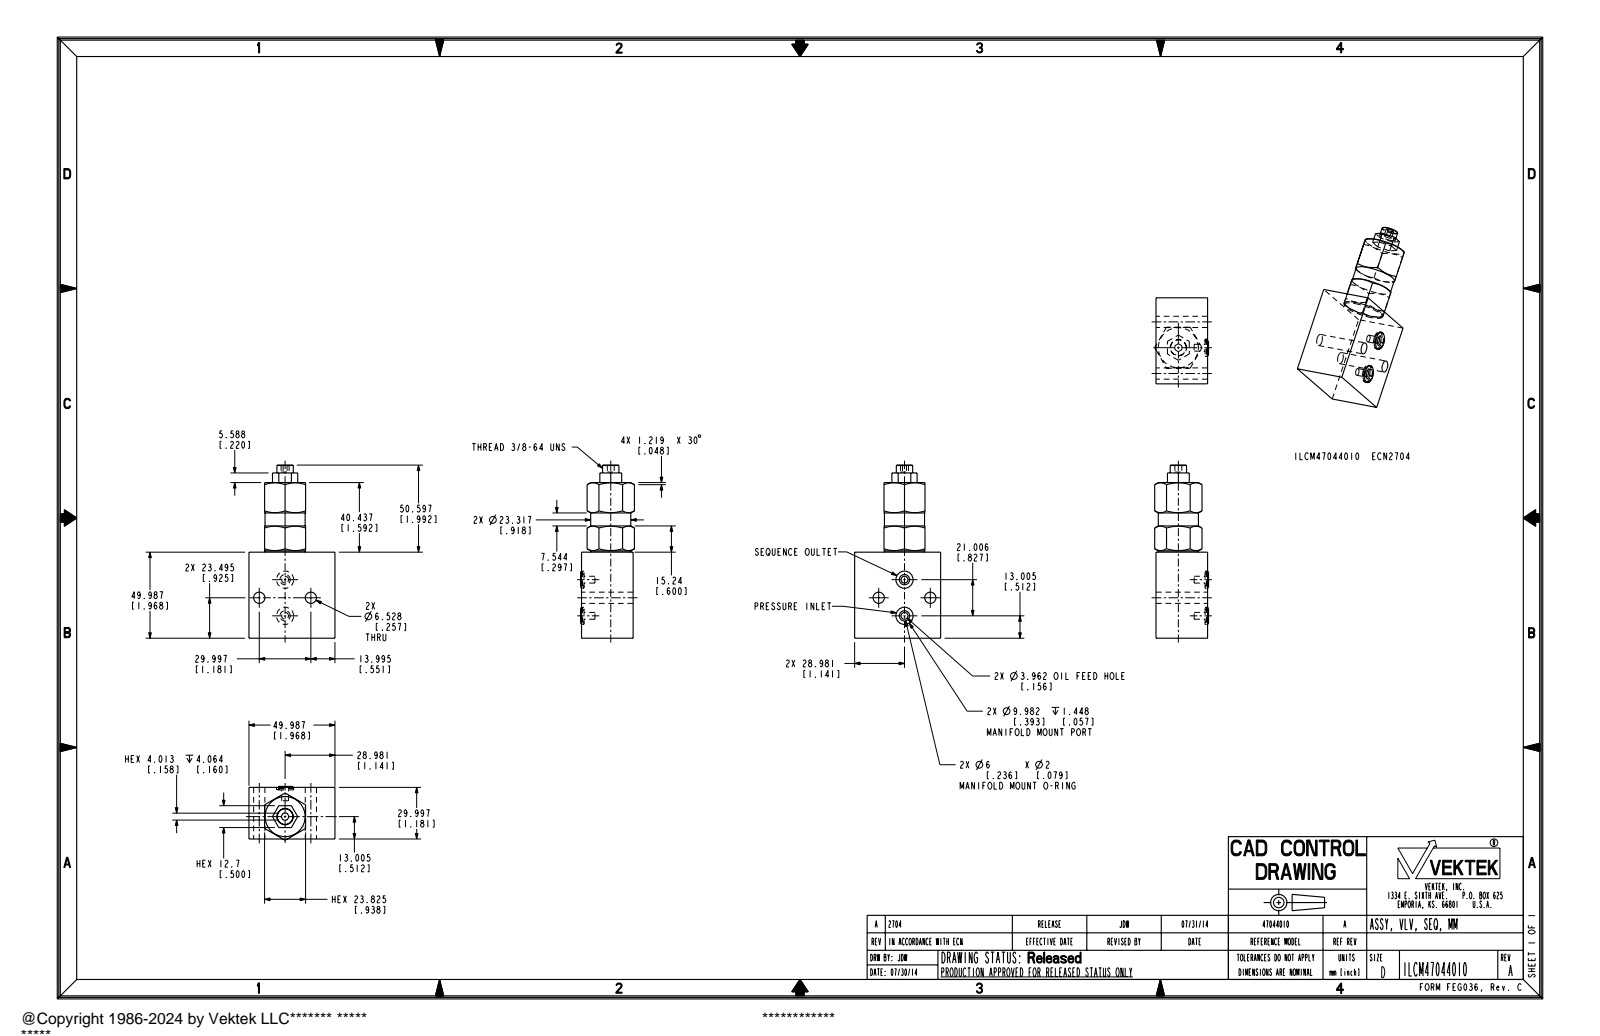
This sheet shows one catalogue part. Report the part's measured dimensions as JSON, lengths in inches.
{"part_name": "ILCM47044010", "step_written_by": "PRO/ENGINEER BY PARAMETRIC TECHNOLOGY CORPORATION, 2013320 (AUTOMOTIVE_DESIGN)", "units": "inches", "bodies": {"solids": 1, "faces": 75, "planar": 39, "cylindrical": 22, "other": 14}, "overall_size": [3.96, 1.968, 1.233], "volume_in3": 5.676, "surface_area_in2": 25.49, "round_holes": [[0.156, 2], [0.257, 2], [0.393, 2]], "round_bosses_or_shafts": [[0.918, 1], [0.374, 1]], "face_to_face_distances": [1.968, 1.181, 0.938, 0.358, 1.296, 1.61, 0.672, 3.56, 1.592, 1.124], "hole_center_spacings": [0.721, 0.72, 0.721, 0.827, 1.181]}
